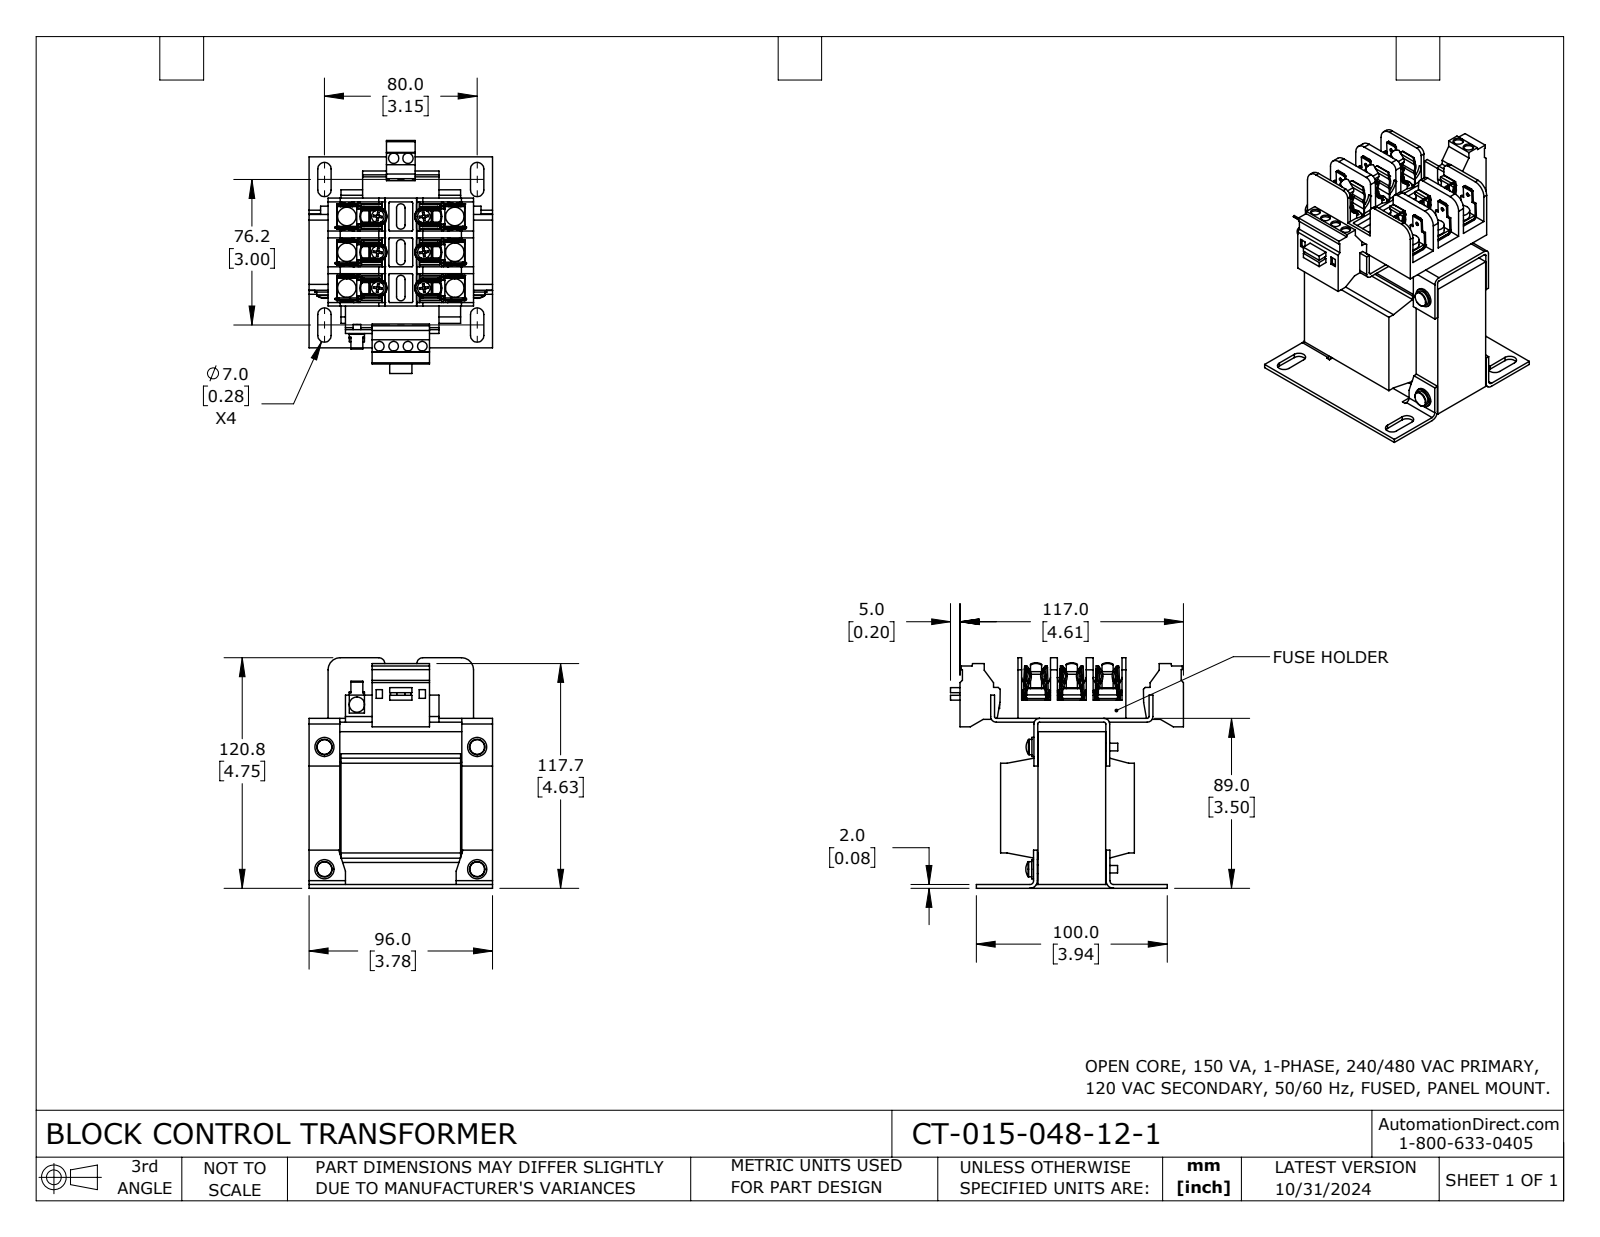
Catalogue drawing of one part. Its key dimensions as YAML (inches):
part_name: "CT-015-048-12-1"
step_written_by: "SolidWorks 2023 (CONFIG_CONTROL_DESIGN)"
units: inches
bodies: {solids: 2, faces: 1602, planar: 1033, cylindrical: 527, other: 42}
overall_size: [4.803, 4.754, 3.78]
volume: 30.49
surface_area: 194.6
round_holes:
  - {diameter: 0.074, count: 12}
  - {diameter: 0.205, count: 5}
  - {diameter: 0.197, count: 4}
  - {diameter: 0.213, count: 2}
  - {diameter: 0.205, count: 1}
round_bosses_or_shafts:
  - {diameter: 0.38, count: 6}
  - {diameter: 0.19, count: 6}
  - {diameter: 0.315, count: 5}
  - {diameter: 0.157, count: 5}
  - {diameter: 0.394, count: 4}
  - {diameter: 0.177, count: 4}
partial_cylinders:
  - {radius: 0.01, count: 24}
  - {radius: 0.05, count: 20}
  - {radius: 0.03, count: 18}
  - {radius: 0.072, count: 14}
  - {radius: 0.038, count: 12}
  - {radius: 0.04, count: 12}
  - {radius: 0.164, count: 12}
  - {radius: 0.097, count: 9}
face_to_face_distances: [0.079, 3.425, 3.504, 3.15, 0.657, 3.122, 0.63, 3.346, 0.738, 1.398]
hole_center_spacings: [2.232, 2.354, 0.026, 0.026, 0.052, 0.295, 0.738, 1.539]
